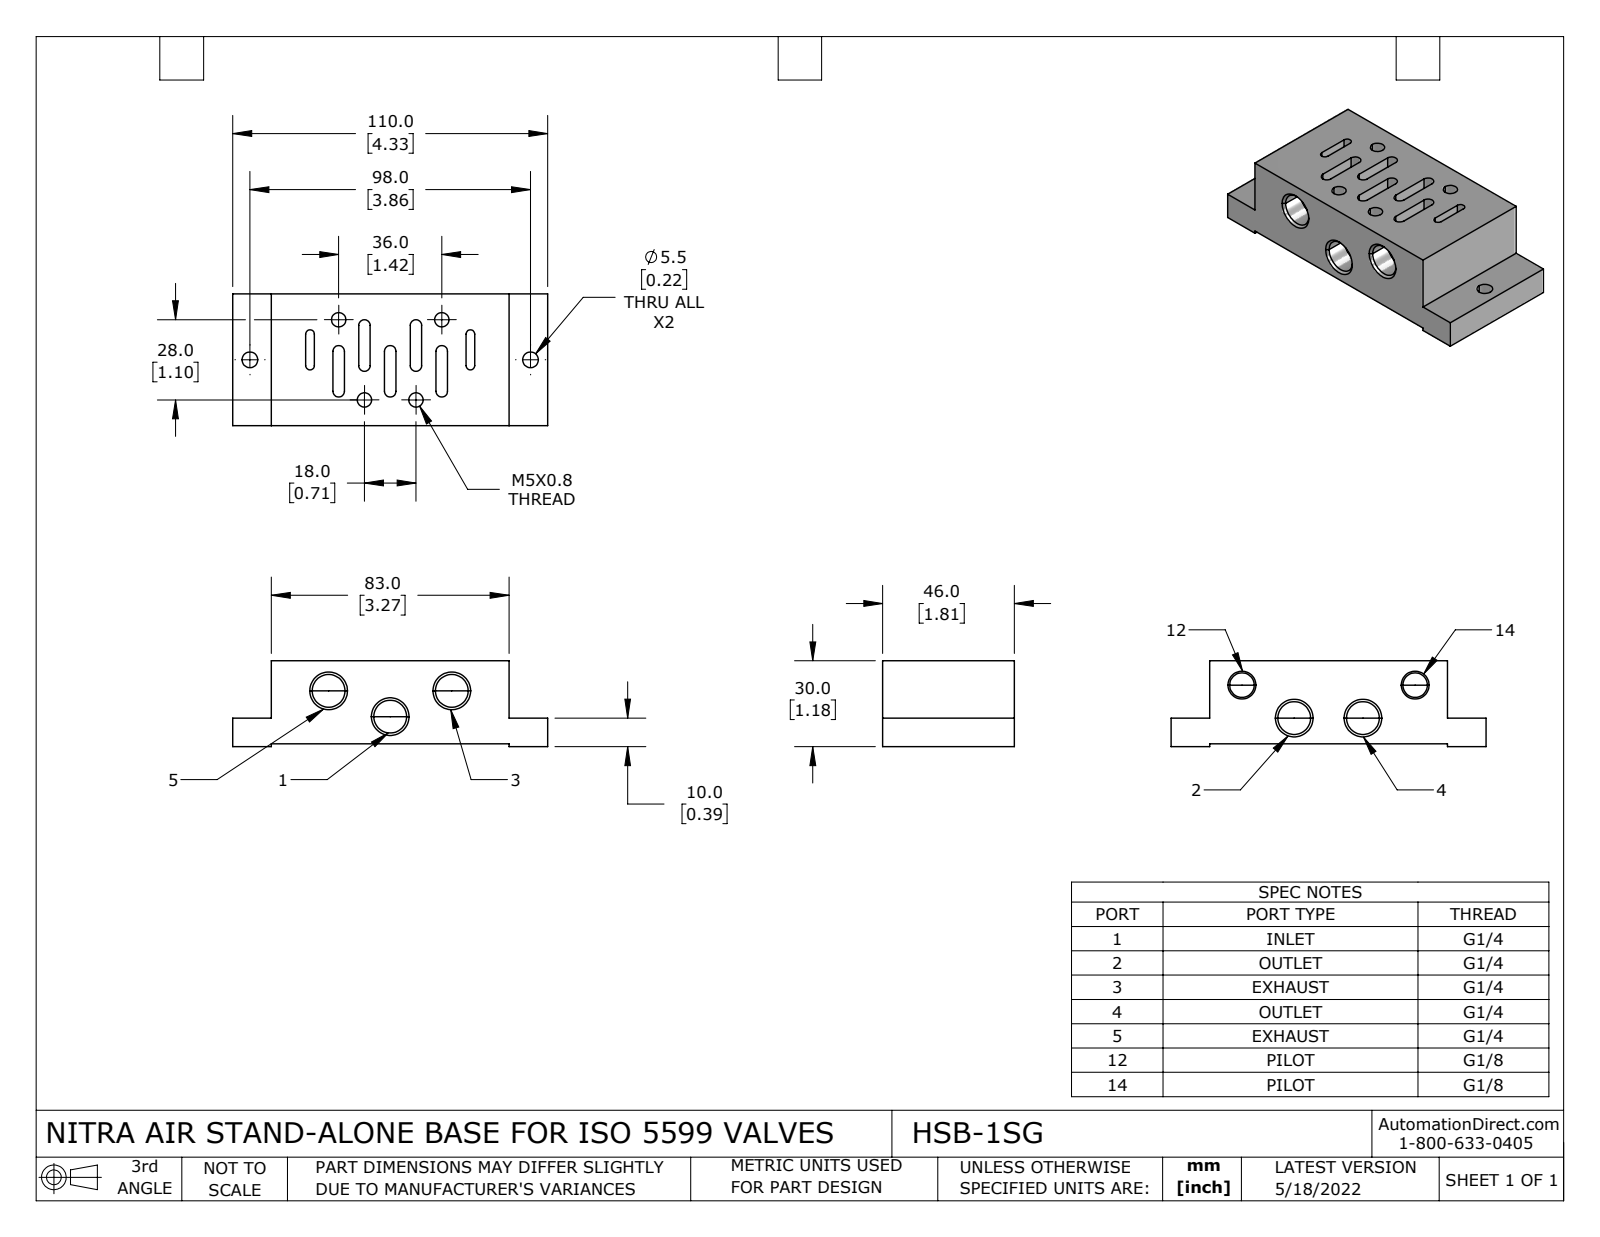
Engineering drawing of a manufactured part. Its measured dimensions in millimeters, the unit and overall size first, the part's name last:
Units: millimetres
Overall size (bounding box): 110 × 46 × 30
Round holes (diameter × count): ⌀11.45 ×5, ⌀5 ×4, ⌀5.5 ×2, ⌀8.57 ×2
Partial cylindrical surfaces — rounded edges, fillets, slot ends (radius × count): R2 ×10, R1.5 ×4
Main face-to-face distances: 29, 46, 9, 1, 10, 30, 20, 13.5, 83, 96.5
Hole centre spacings: 8.98, 12.01, 13.44, 21.57, 23.31, 29.41, 32.19, 34.01
Volume: 112 739 mm³ · Surface area: 22 817 mm²
Bodies: 1 solid, 107 faces (39 planar, 40 cylindrical, 28 other)
Part name (STEP PRODUCT): HSB-1SG
STEP written by: SolidWorks 2021 (CONFIG_CONTROL_DESIGN)
